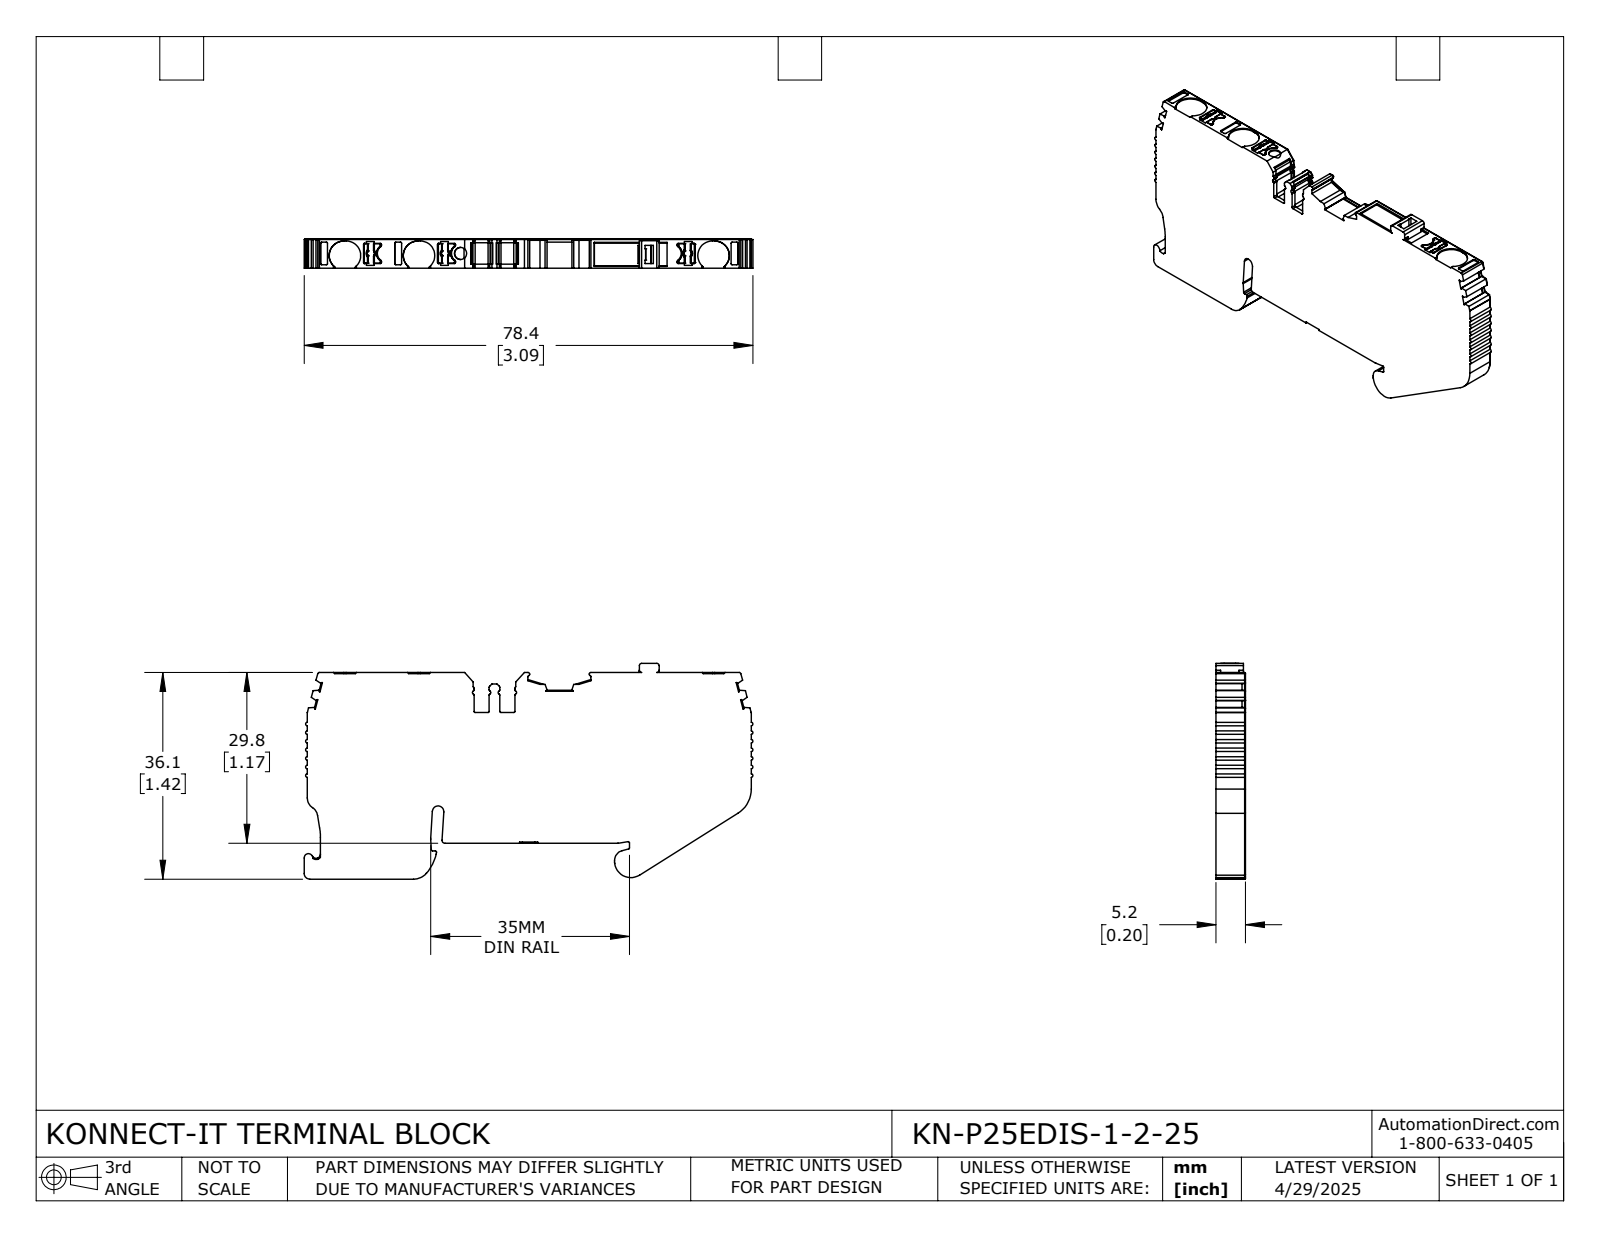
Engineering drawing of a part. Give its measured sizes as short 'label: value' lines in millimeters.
name: KN-P25EDIS-1-2-25
written by: SolidWorks 2024 (CONFIG_CONTROL_DESIGN)
unit: mm
bodies: 1 solid, 691 faces (368 planar, 272 cylindrical, 51 other)
size: 78.36 × 37.67 × 5.15
volume: 11 990 mm³; area: 6 259 mm²
holes: 1× ⌀2.1
rounds: 66× R0.2, 39× R0.3, 19× R0.1, 18× R0.5, 13× R0.4, 12× R0.15, 6× R2.55, 4× R1
face distances: 5.15, 29.61, 29.81, 6.26, 35.87, 36.07, 77.52, 1.2, 5, 4.5
